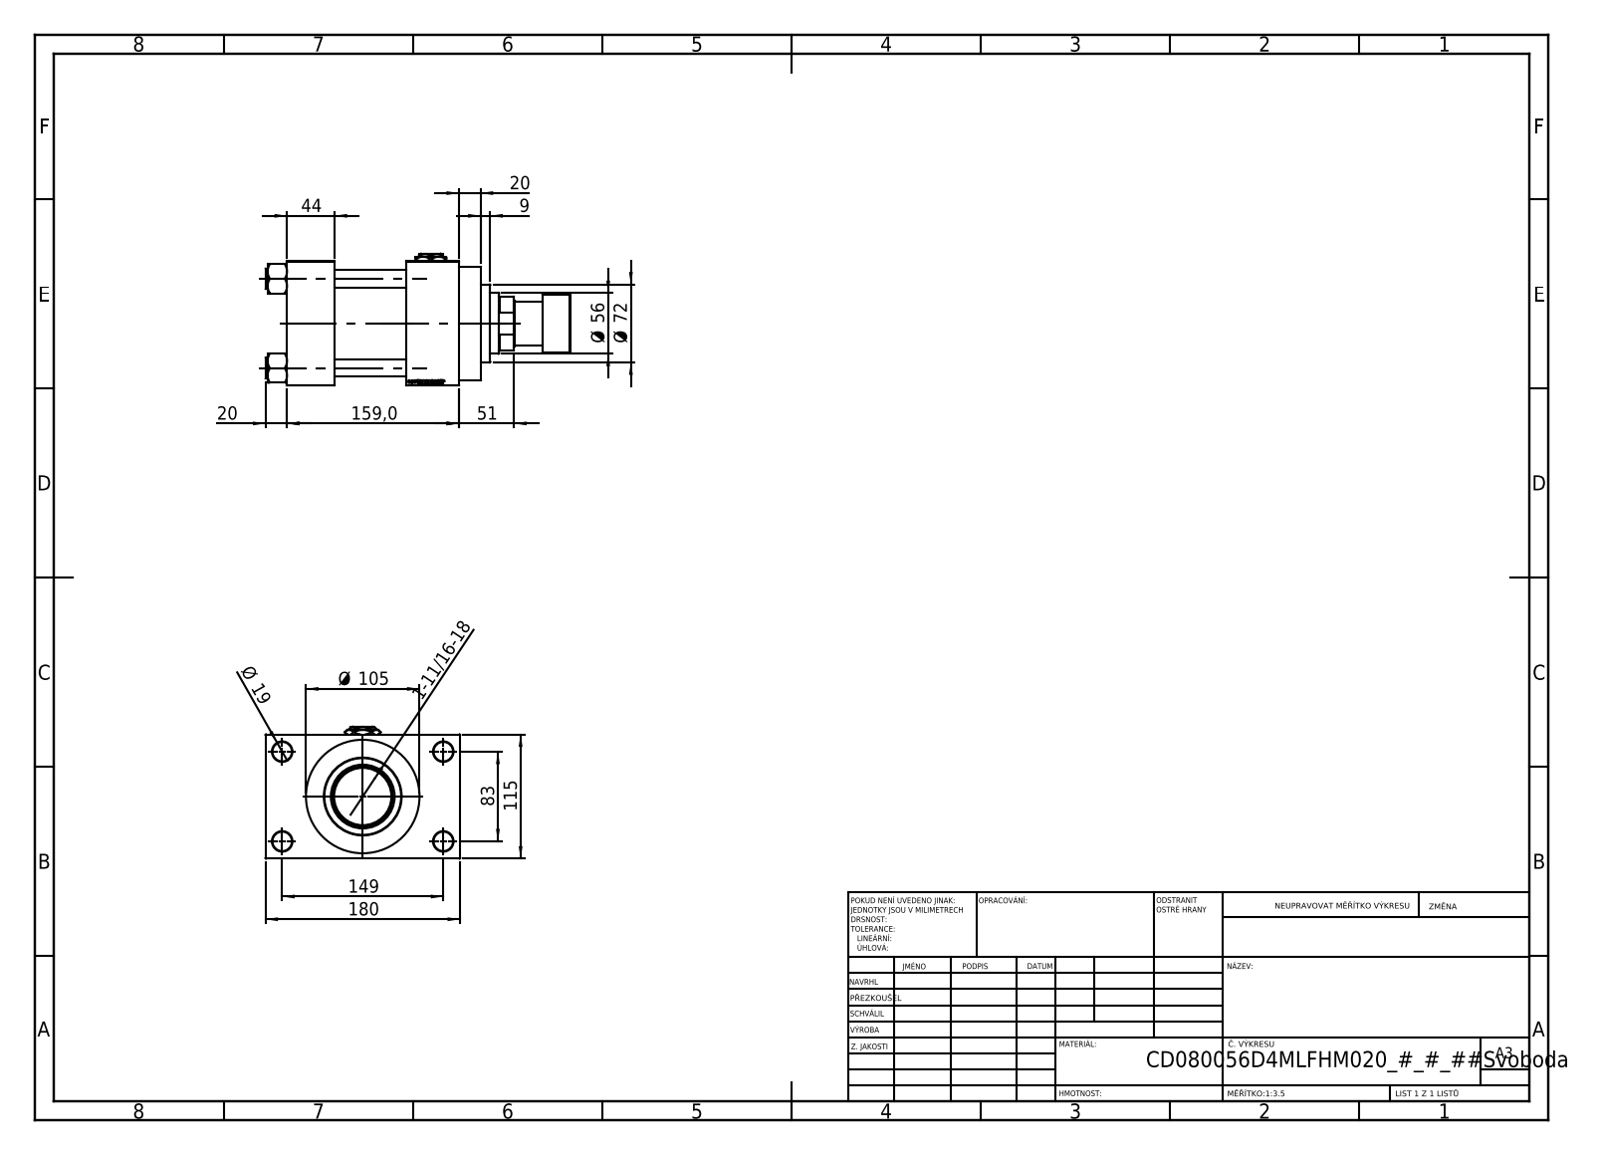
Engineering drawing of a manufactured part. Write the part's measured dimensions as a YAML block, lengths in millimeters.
part_name: "V215CD_D_TYCINKA; V215CD_D_Body; V215CR_ROD_END_F; V215CD_VC_A (+3 more)"
step_written_by: "SolidWorks 2019 (CONFIG_CONTROL_DESIGN)"
units: millimeters
bodies: {solids: 13, faces: 1205, planar: 570, cylindrical: 91, other: 544}
overall_size: [282, 180, 122]
volume: 2216000
surface_area: 322595
round_holes:
  - {diameter: 16, count: 4}
  - {diameter: 18, count: 4}
  - {diameter: 7, count: 2}
  - {diameter: 26.44, count: 2}
  - {diameter: 35, count: 2}
  - {diameter: 40.5, count: 1}
  - {diameter: 56, count: 1}
  - {diameter: 59, count: 1}
  - {diameter: 61, count: 1}
  - {diameter: 72, count: 1}
  - {diameter: 80, count: 1}
round_bosses_or_shafts:
  - {diameter: 19, count: 4}
  - {diameter: 105, count: 1}
  - {diameter: 86, count: 1}
  - {diameter: 54, count: 1}
  - {diameter: 40, count: 1}
face_to_face_distances: [115, 66, 110, 44, 32.5, 159, 49, 147.5, 20, 69]
hole_center_spacings: [33.15, 58.48, 82.7, 85.28, 89.24, 115.85, 142.43, 83]
